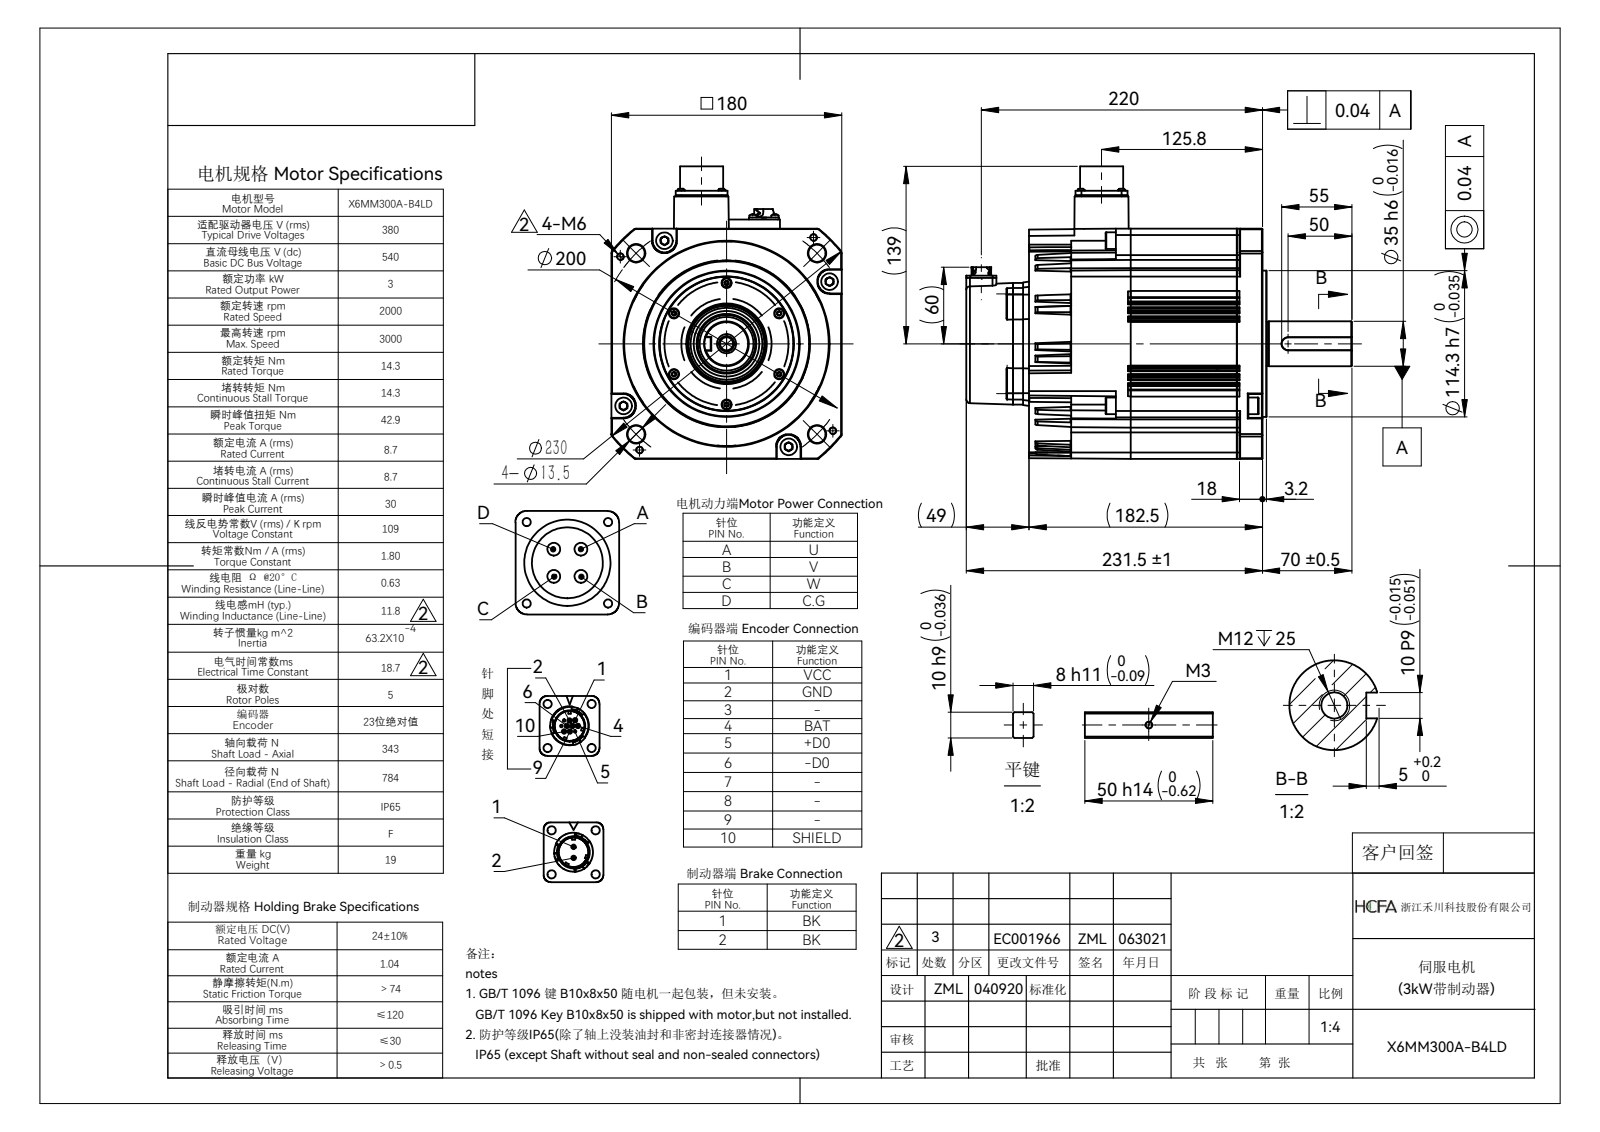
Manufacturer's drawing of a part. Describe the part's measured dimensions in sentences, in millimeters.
The part is named "SV-X6MM300A-B4LD". Its 3-D file was written by "SolidWorks 2016 (CONFIG_CONTROL_DESIGN)". It is 1 solid with 2070 faces: 793 planar, 748 cylindrical and 529 other. Overall it measures 301.5 by 228.55 by 180 millimeters. Its volume is 5 455 000 cubic millimeters and its surface area 264 645 square millimeters. Round holes: 4 of diameter 13.5, 2 of diameter 2.5, 2 of diameter 3, 1 of diameter 10.2, 1 of diameter 11.6, 1 of diameter 11.75, 1 of diameter 27.7, 1 of diameter 32.5, 1 of diameter 92. Round bosses or shafts: 4 of diameter 13, 4 of diameter 5.7, 4 of diameter 5.6, 4 of diameter 5, 4 of diameter 3, 2 of diameter 15.2, 2 of diameter 0.75, 1 of diameter 114.3. Partial cylindrical surfaces (rounded edges, fillets, slot ends): 98 of radius 0.5, 42 of radius 1, 29 of radius 5, 18 of radius 2, 12 of radius 3, 8 of radius 2.8, 6 of radius 0.32, 6 of radius 1.15. The main face-to-face distances are 180, 32.5, 182.5, 147.5, 185.7, 3.2, 49, 231.5, 234.7, 115. The hole center spacings are 100, 141.42, 200, 17.2, 48.75, 103.13, 104.6, 106.34.
